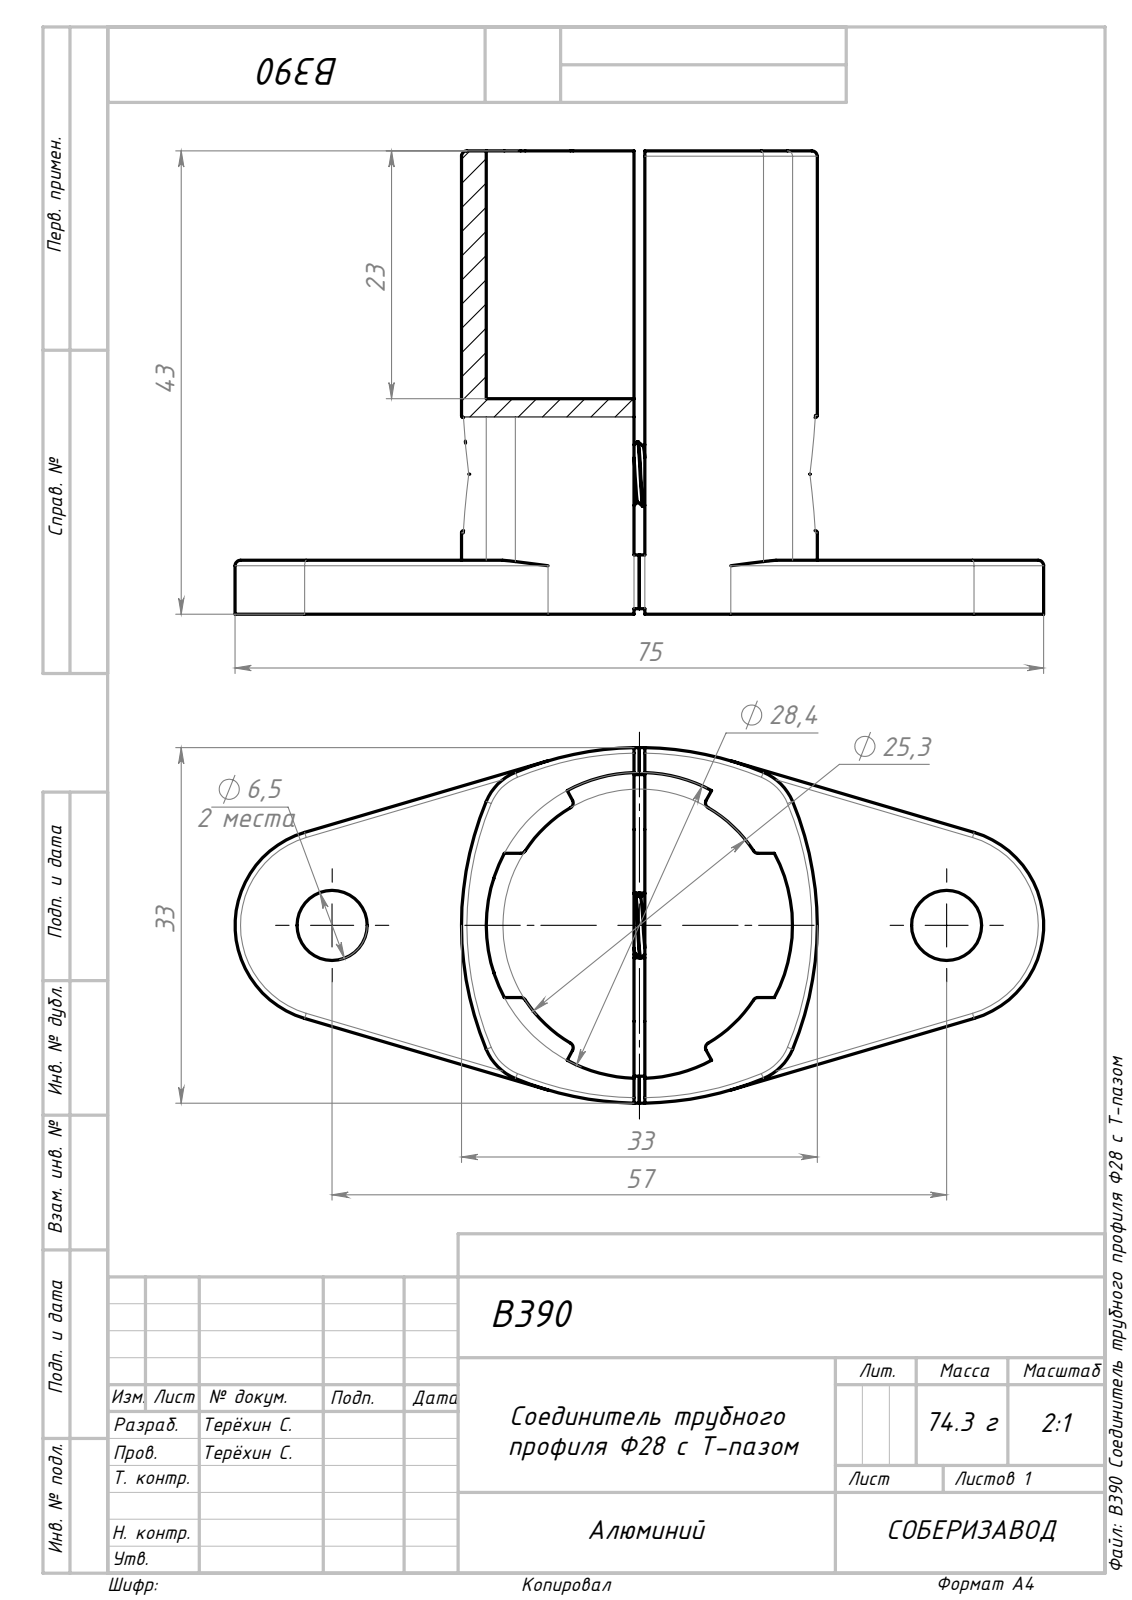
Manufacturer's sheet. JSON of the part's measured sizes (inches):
{"part_name": "B390 Соединитель трубного профиля Ф28 с Т-пазом_00; B390 Соединитель трубного профиля Ф28 с Т-пазом", "step_written_by": "SolidWorks 2025 (CONFIG_CONTROL_DESIGN)", "units": "inches", "bodies": {"solids": 3, "faces": 311, "planar": 110, "cylindrical": 116, "other": 85}, "overall_size": [2.953, 1.693, 1.299], "volume_in3": 1.606, "surface_area_in2": 23.94, "round_holes": [[0.256, 3], [0.205, 1], [1.118, 1]], "round_bosses_or_shafts": [[0.394, 1], [0.236, 1]], "partial_cylinders_radius": [[0.02, 28], [0.197, 4], [1.181, 4], [0.354, 2], [1.083, 2], [0.498, 1]], "face_to_face_distances": [0.197, 0.787, 0.236, 0.276, 0.591, 0.039, 0.512, 0.413, 0.906, 1.496], "hole_center_spacings": [1.181, 2.362]}
